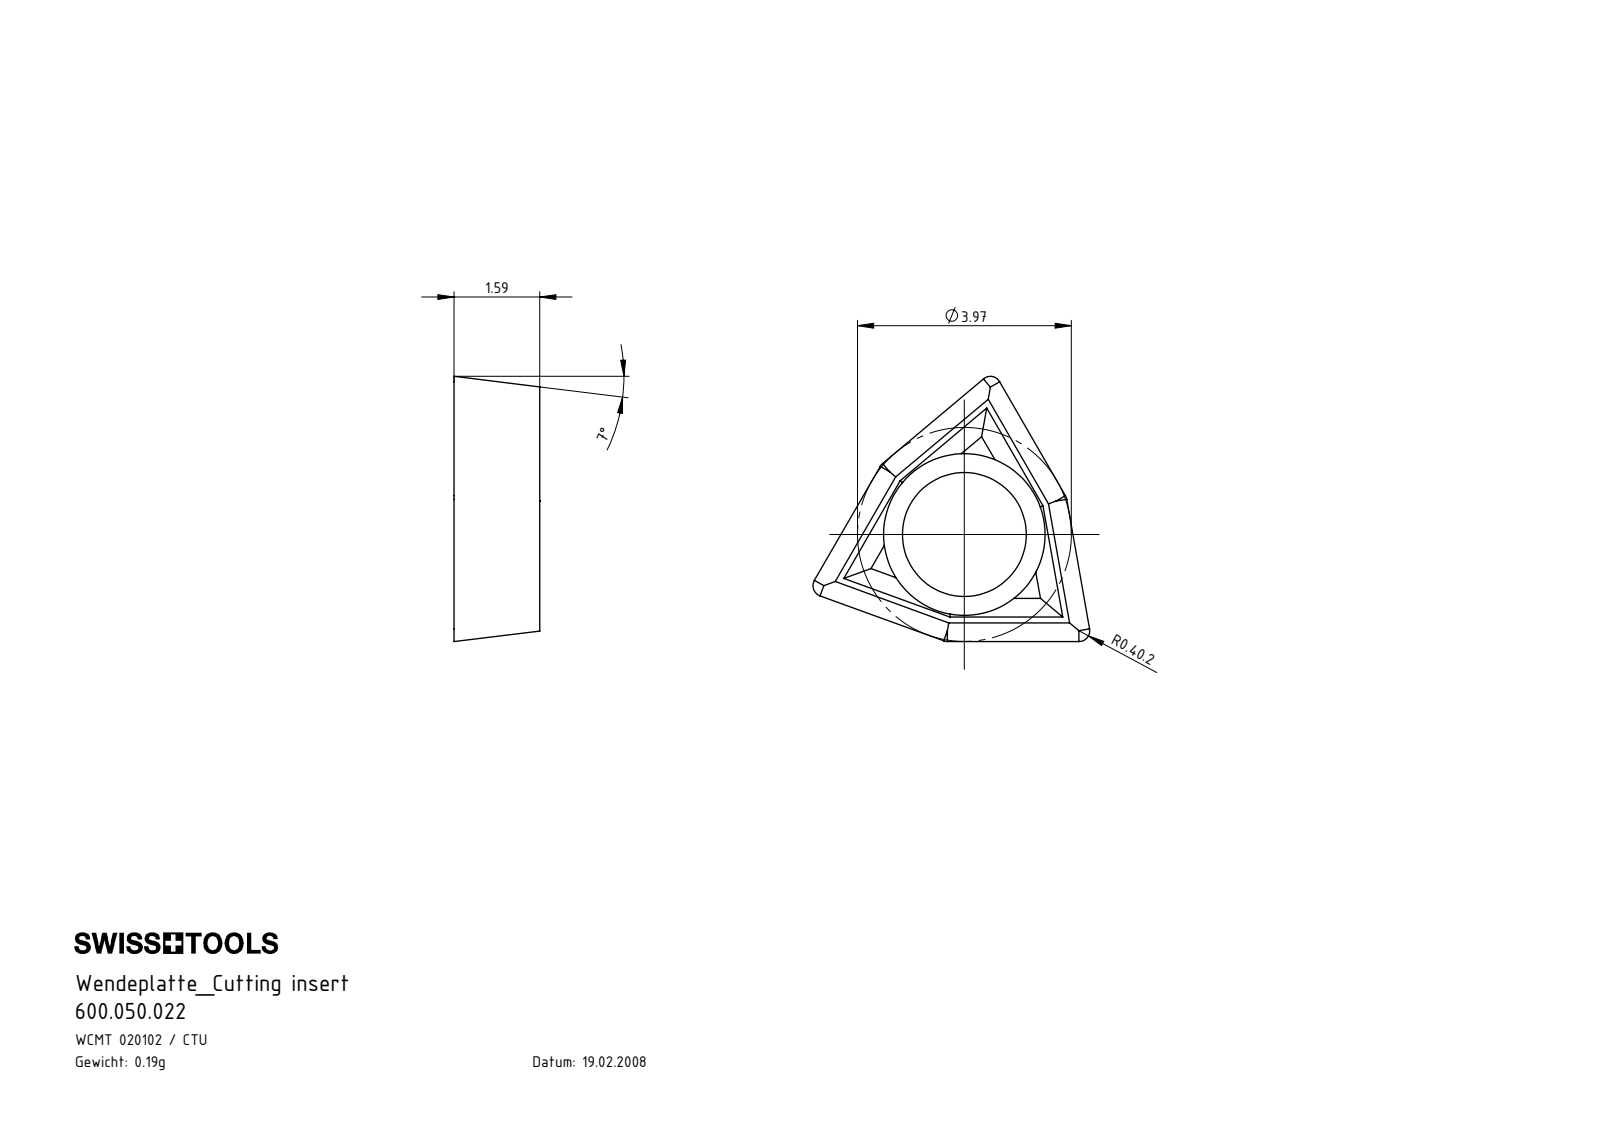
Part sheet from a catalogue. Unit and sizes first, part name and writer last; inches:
Units: inches
Overall size (bounding box): 0.202 × 0.194 × 0.063
Round holes (diameter × count): ⌀0.091 ×1, ⌀0.118 ×1
Main face-to-face distances: 0.055, 0.063
Volume: 0.001 in³ · Surface area: 0.088 in²
Bodies: 1 solid, 43 faces (23 planar, 4 cylindrical, 16 other)
Part name (STEP PRODUCT): 600.050.022
STEP written by: SolidWorks 2022 (AUTOMOTIVE_DESIGN)
